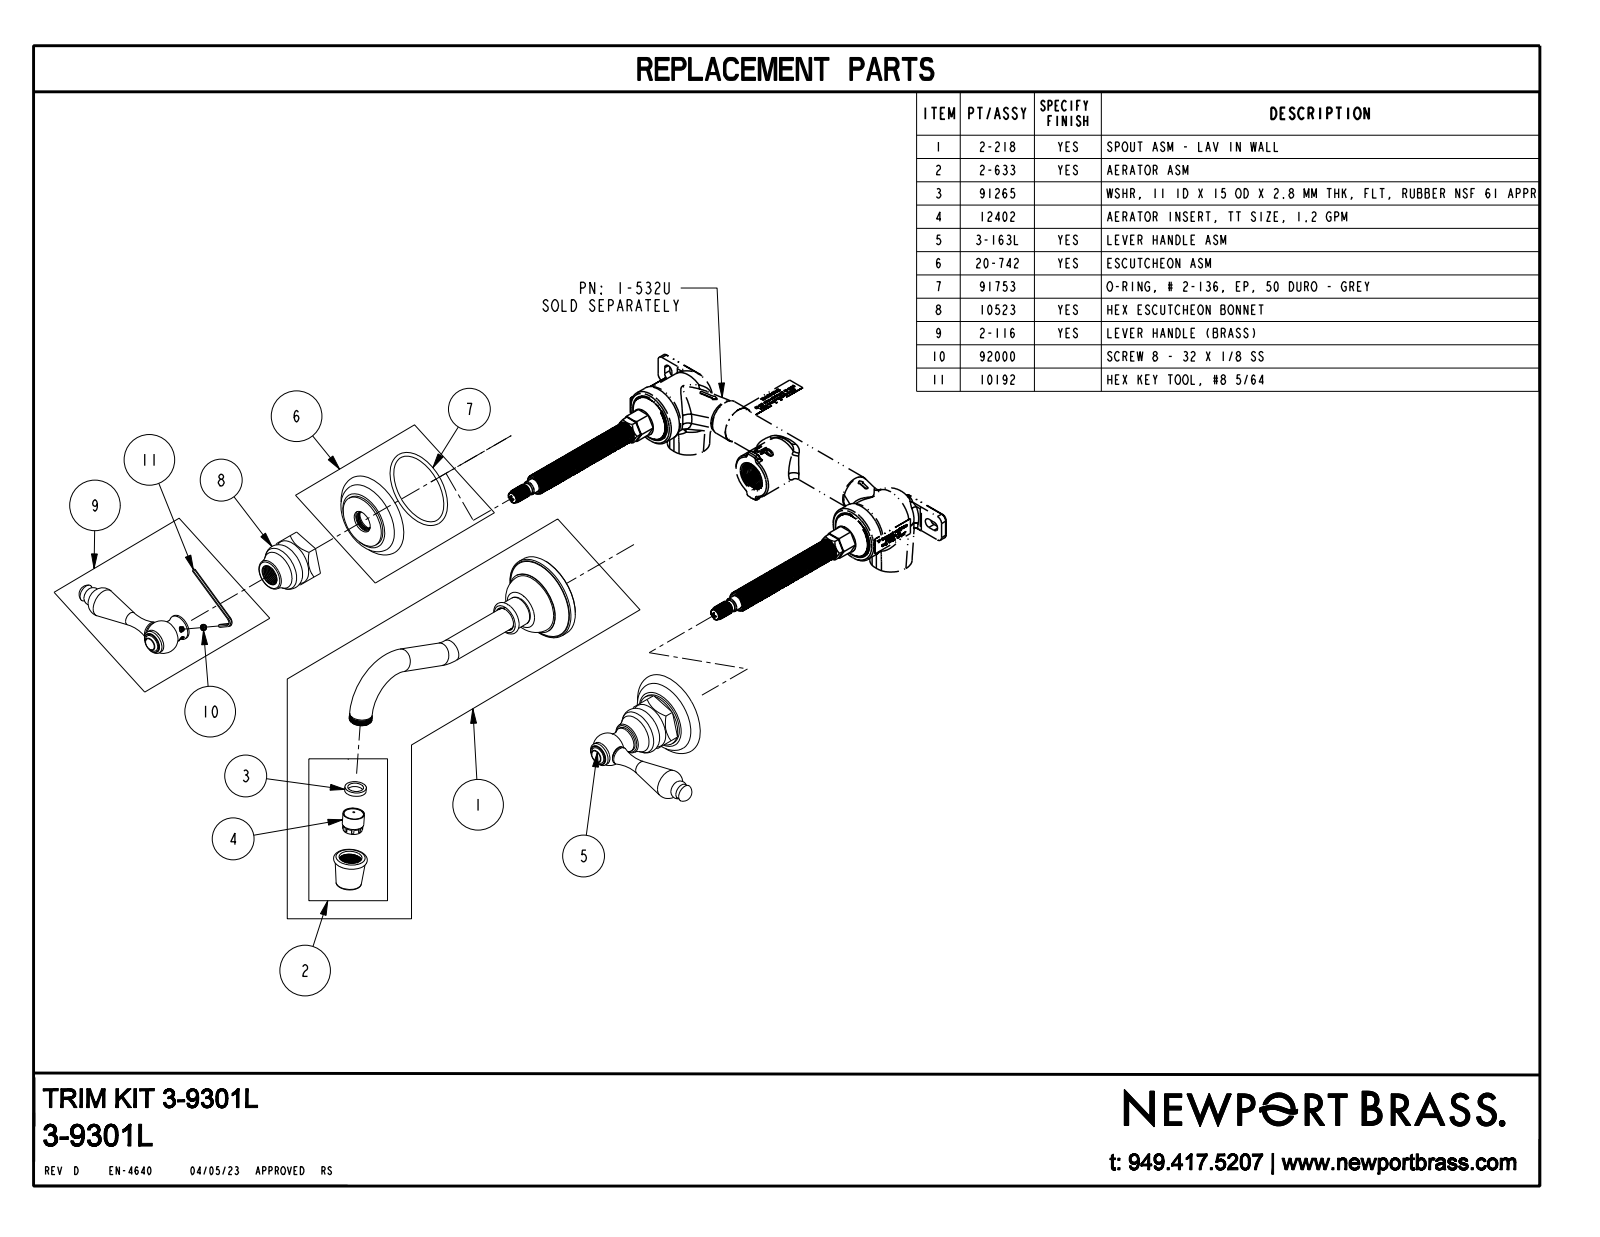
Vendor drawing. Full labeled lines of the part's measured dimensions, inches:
Part name (STEP PRODUCT): 3-9301L_SW
STEP written by: CREO PARAMETRIC BY PTC INC, 2018400 (AUTOMOTIVE_DESIGN)
Units: inches
Bodies: 3 solids, 197 faces (61 planar, 34 cylindrical, 102 other)
Overall size (bounding box): 14.15 × 7.645 × 2.445
Volume: 13.12 in³ · Surface area: 73.83 in²
Round bosses / shafts (diameter × count): ⌀1.482 ×2, ⌀0.705 ×2, ⌀0.661 ×2, ⌀0.625 ×2, ⌀0.548 ×2, ⌀0.544 ×2, ⌀2.36 ×1, ⌀1.764 ×1
Main face-to-face distances: 0.375, 1.687, 1.312, 0.96, 0.585, 0.727, 1.313, 5.569, 2.04, 1.313
